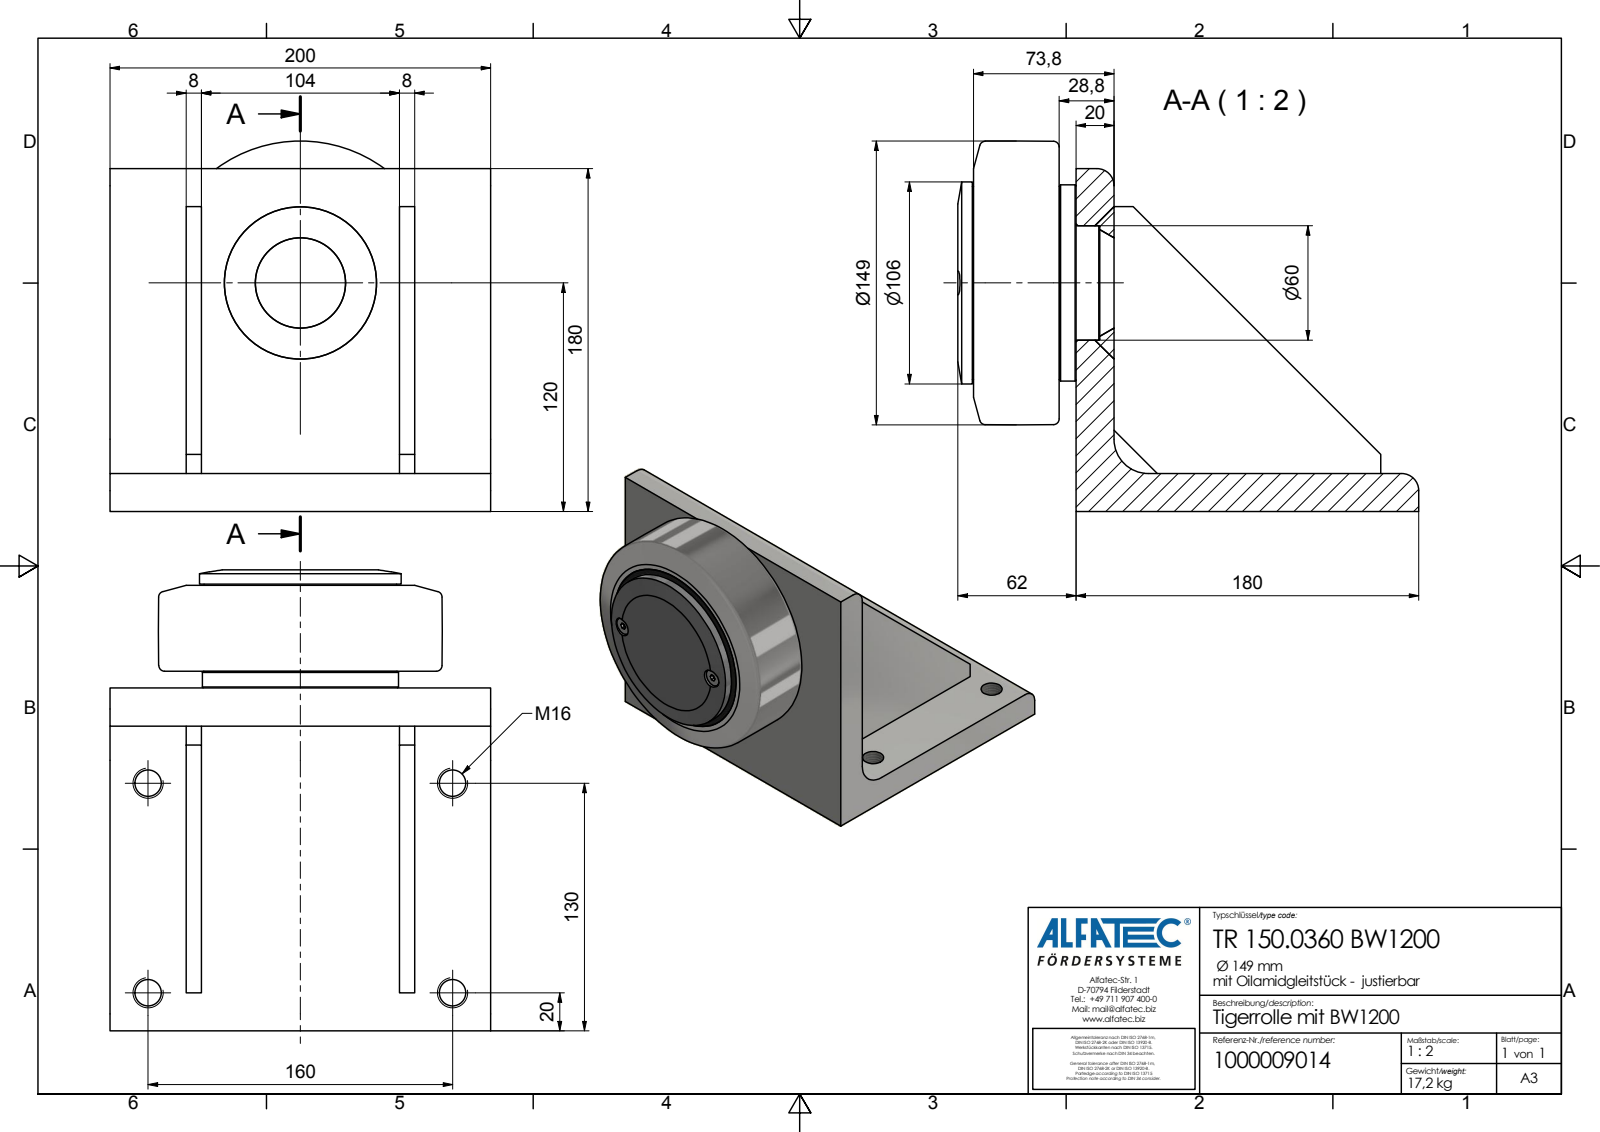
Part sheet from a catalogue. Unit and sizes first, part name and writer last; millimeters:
Units: millimetres
Overall size (bounding box): 242 × 200 × 194.5
Round holes (diameter × count): ⌀13.84 ×4, ⌀12.4 ×2
Round bosses / shafts (diameter × count): ⌀11.7 ×2, ⌀106 ×1, ⌀103 ×1, ⌀101.4 ×1, ⌀101.2 ×1
Partial cylindrical surfaces — rounded edges, fillets, slot ends (radius × count): R9 ×2, R18 ×1
Main face-to-face distances: 20, 8, 112, 160, 40, 48, 152, 104, 120, 8.8
Hole centre spacings: 110, 160, 194.16, 83
Volume: 2 440 000 mm³ · Surface area: 244 501 mm²
Bodies: 1 solid, 65 faces (41 planar, 15 cylindrical, 9 other)
Part name (STEP PRODUCT): TR 150.0360 BW1200_Kontur
STEP written by: Autodesk Inventor 2020 (AP242_MANAGED_MODEL_BASED_3D_ENGINEERING_MIM_LF)
